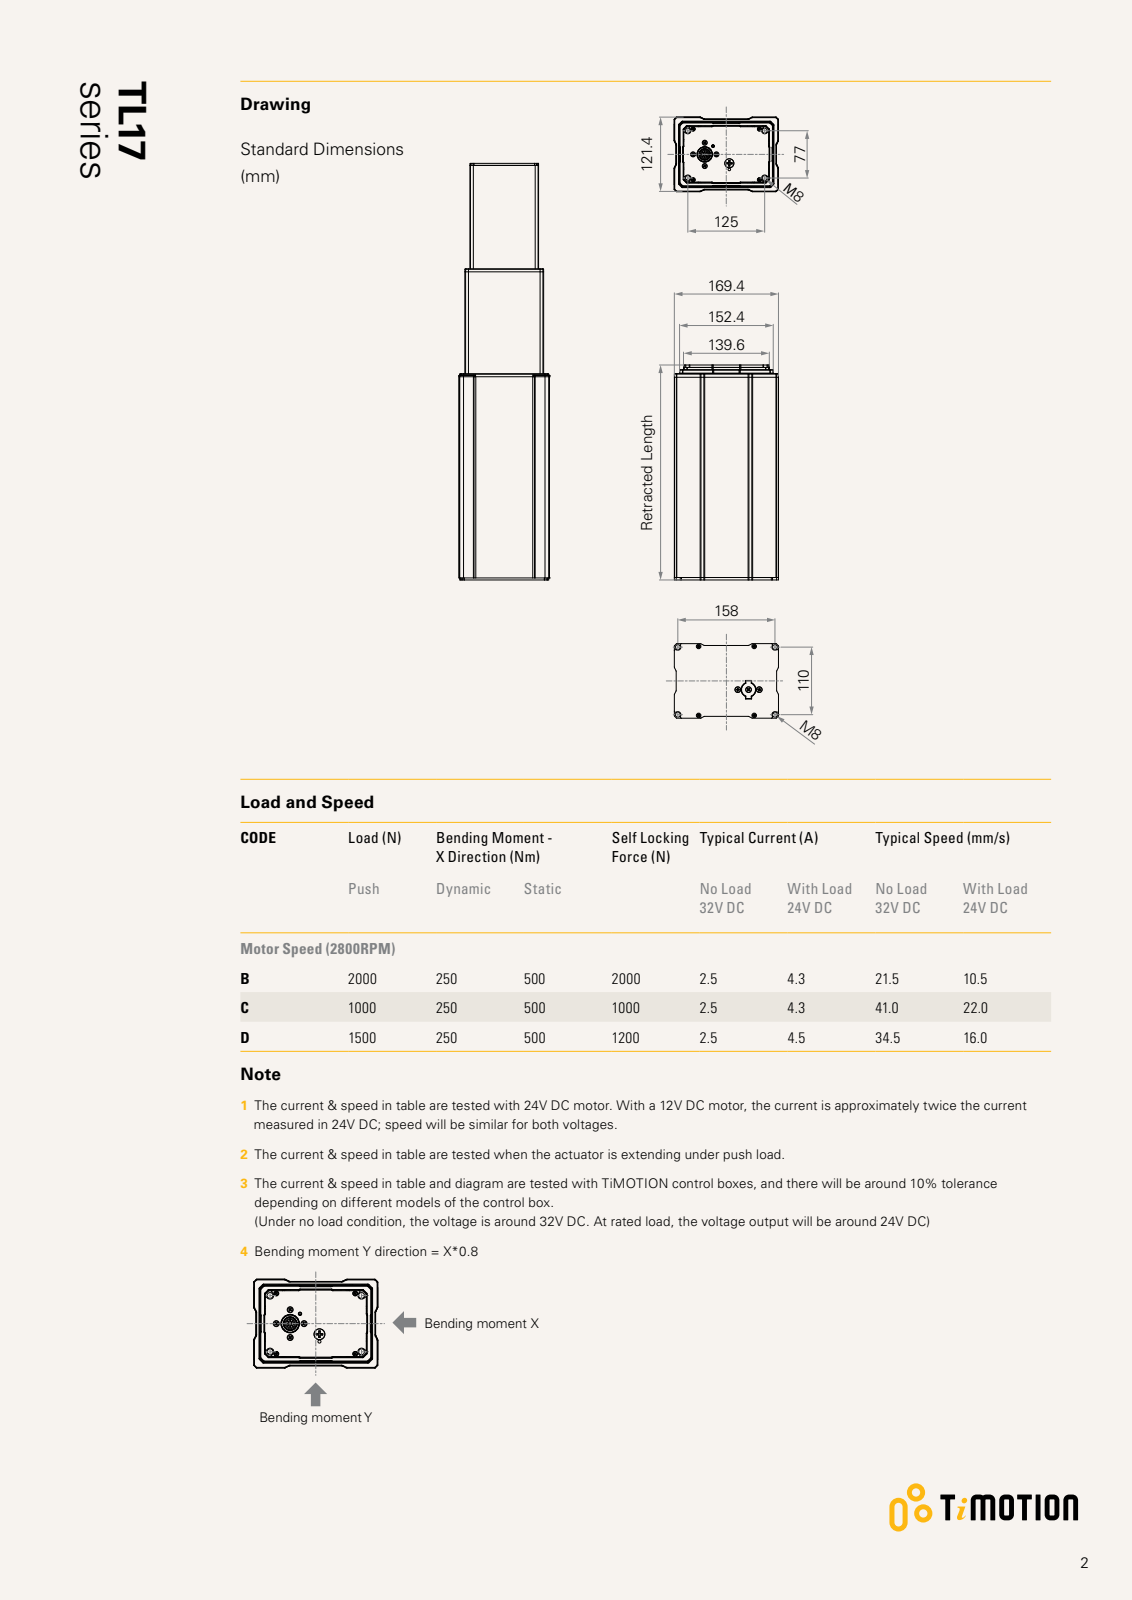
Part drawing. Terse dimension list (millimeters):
name: 3D_TL17
written by: SolidWorks 2015 (CONFIG_CONTROL_DESIGN)
unit: mm
bodies: 4 solids, 830 faces (429 planar, 287 cylindrical, 114 other)
size: 350 × 169.41 × 121.4
volume: 6 846 000 mm³; area: 324 001 mm²
holes: 7× ⌀8, 4× ⌀4.4, 4× ⌀7.5, 4× ⌀10, 2× ⌀4.2, 1× ⌀25.2
rounds: 64× R1, 24× R2, 20× R3, 8× R5, 1× R11.8, 1× R12
face distances: 3, 118.4, 3.9, 4, 121.4, 342.1, 115.4, 346, 346.1, 169.4
hole spacings: 9.03, 19, 26.87, 80.26, 116.44, 141.14, 23.33, 28.59
